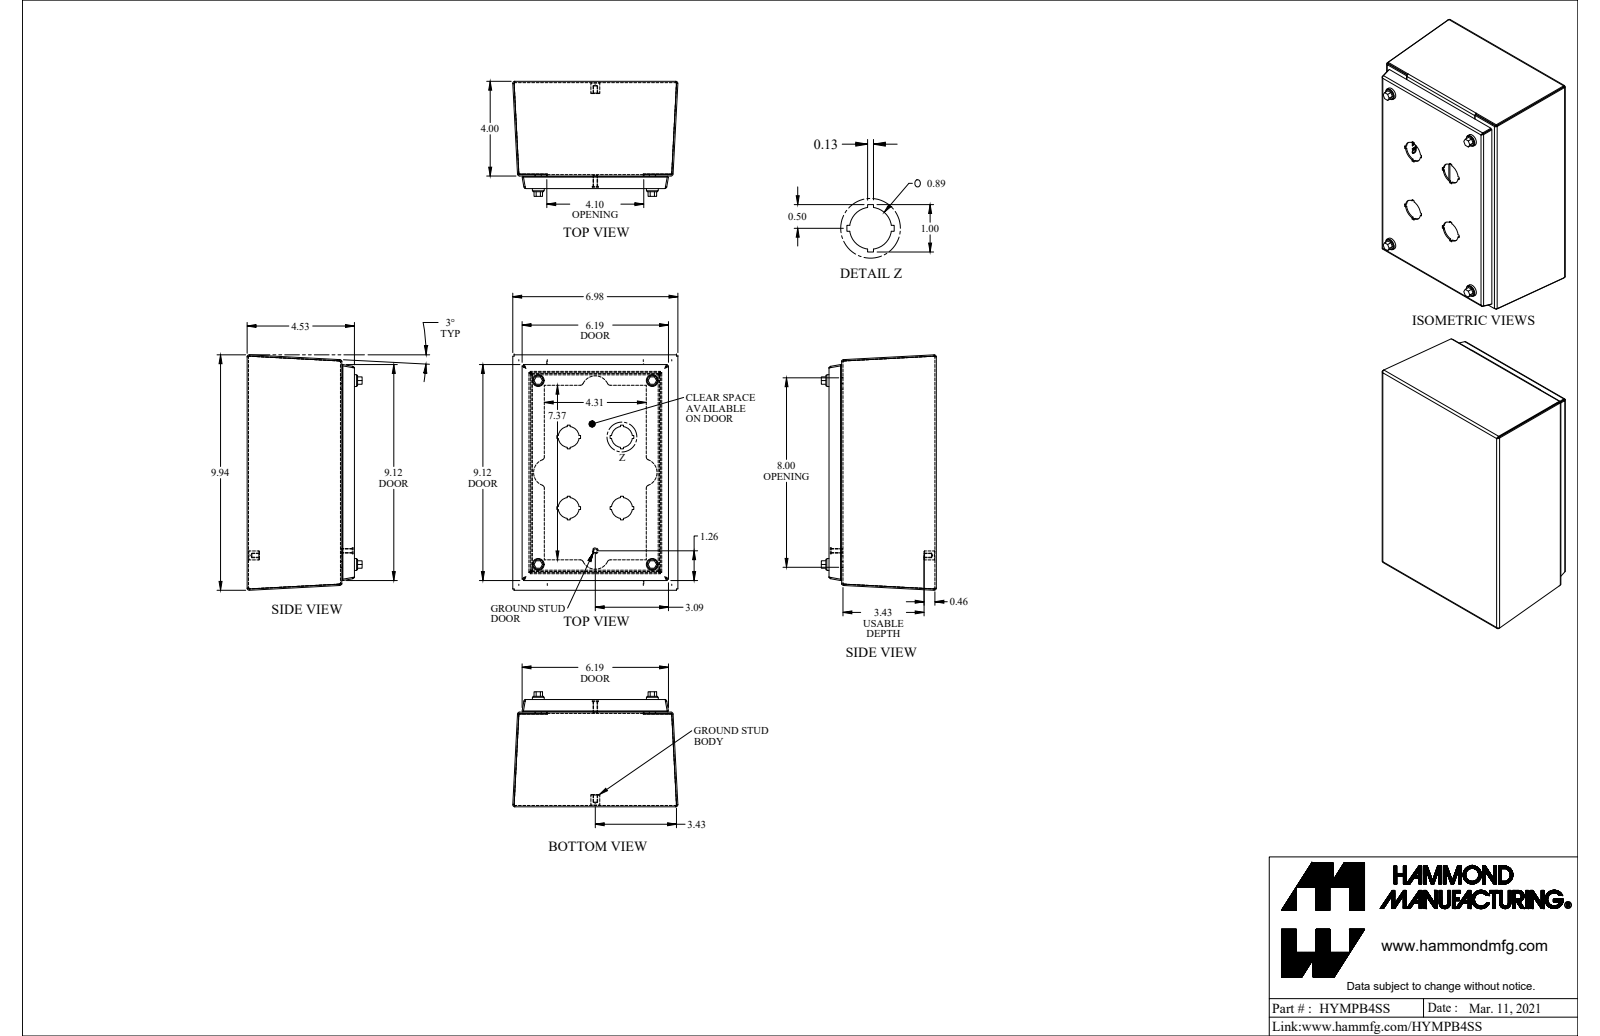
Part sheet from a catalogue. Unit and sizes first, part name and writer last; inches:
Units: inches
Overall size (bounding box): 9.942 × 6.976 × 4.859
Round holes (diameter × count): ⌀0.065 ×4, ⌀0.239 ×4, ⌀0.24 ×4, ⌀0.25 ×4, ⌀0.253 ×4, ⌀0.4 ×4, ⌀0.886 ×4, ⌀0.235 ×2, ⌀0.235 ×2, ⌀0.156 ×1
Round bosses / shafts (diameter × count): ⌀0.375 ×5, ⌀0.19 ×5, ⌀0.5 ×4, ⌀0.45 ×4, ⌀0.406 ×4, ⌀0.315 ×4, ⌀0.25 ×1
Partial cylindrical surfaces — rounded edges, fillets, slot ends (radius × count): R0.029 ×16, R0.086 ×16, R0.125 ×12, R0.055 ×4, R0.076 ×4, R0.5 ×4, R0.575 ×4
Main face-to-face distances: 0.057, 4.418, 4.475, 0.057, 4.532, 4.475, 3.943, 0.475, 4, 0.532
Hole centre spacings: 9.139, 7.766, 7.766, 2.707, 4.819, 4.263, 4.819, 5.534
Volume: 21.58 in³ · Surface area: 695.2 in²
Bodies: 22 solids, 515 faces (344 planar, 148 cylindrical, 23 other)
Part name (STEP PRODUCT): HYMPB4SS
STEP written by: SolidWorks 2021 (AUTOMOTIVE_DESIGN)
